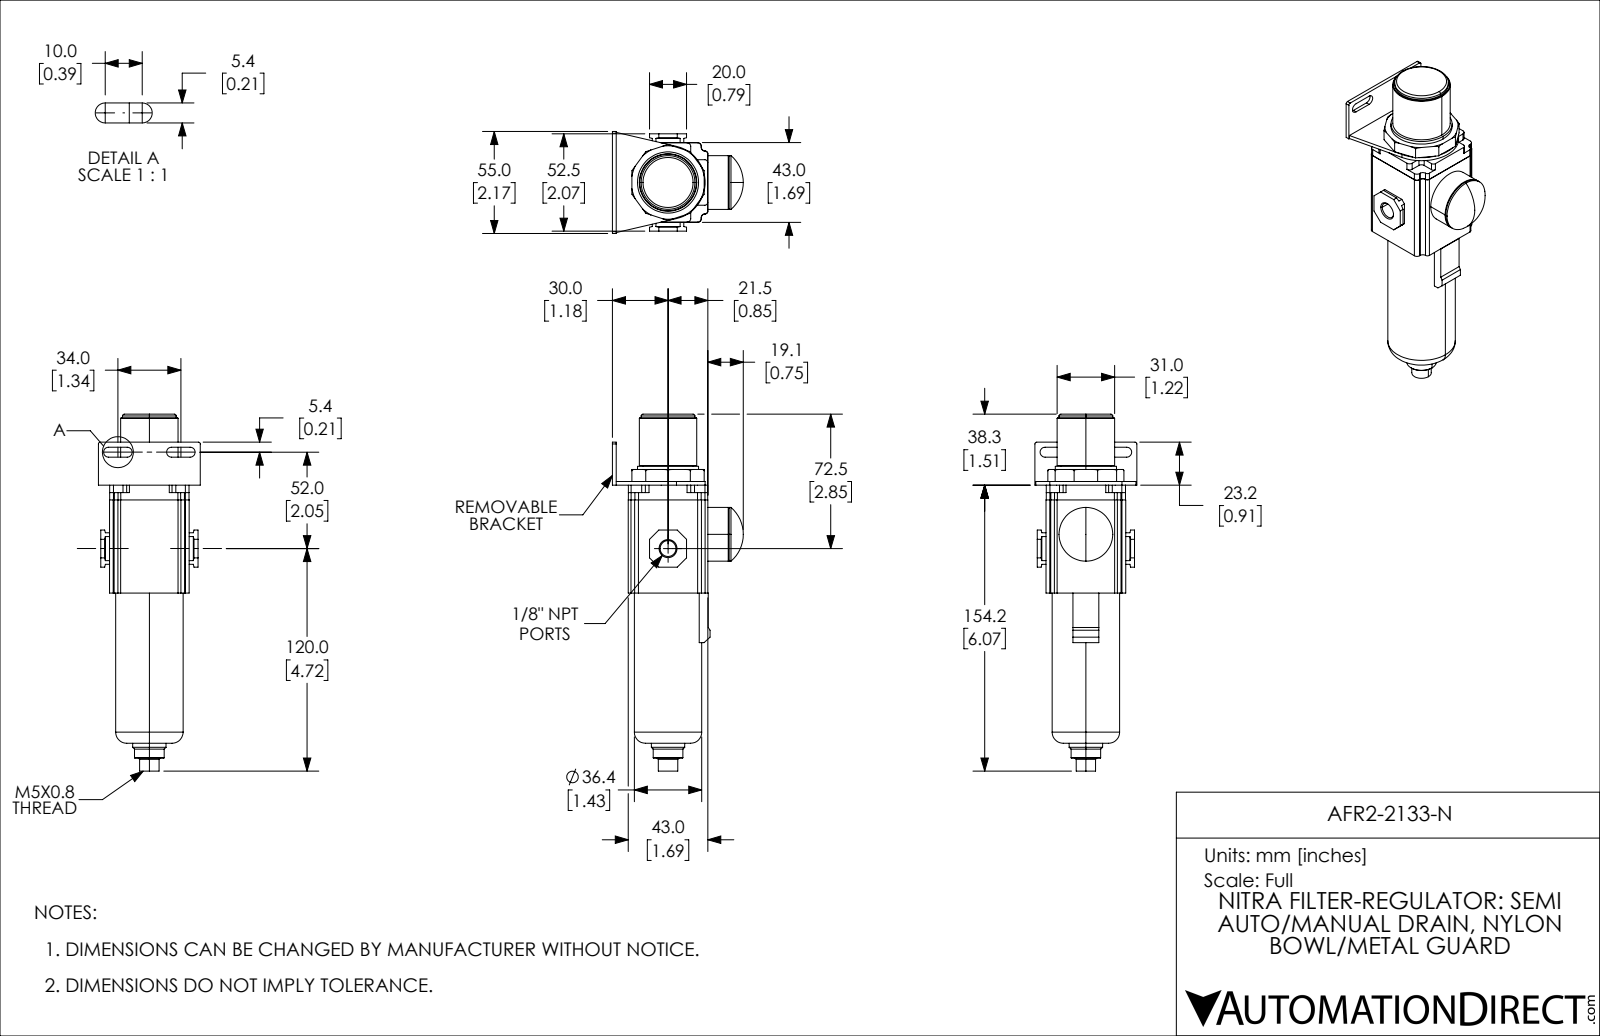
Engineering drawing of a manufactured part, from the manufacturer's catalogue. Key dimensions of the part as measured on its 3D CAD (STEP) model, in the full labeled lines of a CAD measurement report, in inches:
Part name (STEP PRODUCT): AFR2-2133-N
STEP written by: SolidWorks 2019 (CONFIG_CONTROL_DESIGN)
Units: inches
Bodies: 1 solid, 220 faces (119 planar, 69 cylindrical, 32 other)
Overall size (bounding box): 7.579 × 2.78 × 2.165
Volume: 14.58 in³ · Surface area: 52.23 in²
Round holes (diameter × count): ⌀0.163 ×1, ⌀0.337 ×1
Round bosses / shafts (diameter × count): ⌀1.142 ×2, ⌀1.433 ×1, ⌀1.299 ×1, ⌀1.22 ×1, ⌀1.054 ×1, ⌀0.709 ×1, ⌀0.63 ×1, ⌀0.413 ×1
Partial cylindrical surfaces — rounded edges, fillets, slot ends (radius × count): R0.079 ×24, R0.059 ×12, R0.106 ×4, R0.039 ×2, R0.787 ×1
Main face-to-face distances: 1.693, 0.079, 0.335, 0.256, 1.949, 2.028, 1.689, 1.429, 2.291, 2.37
